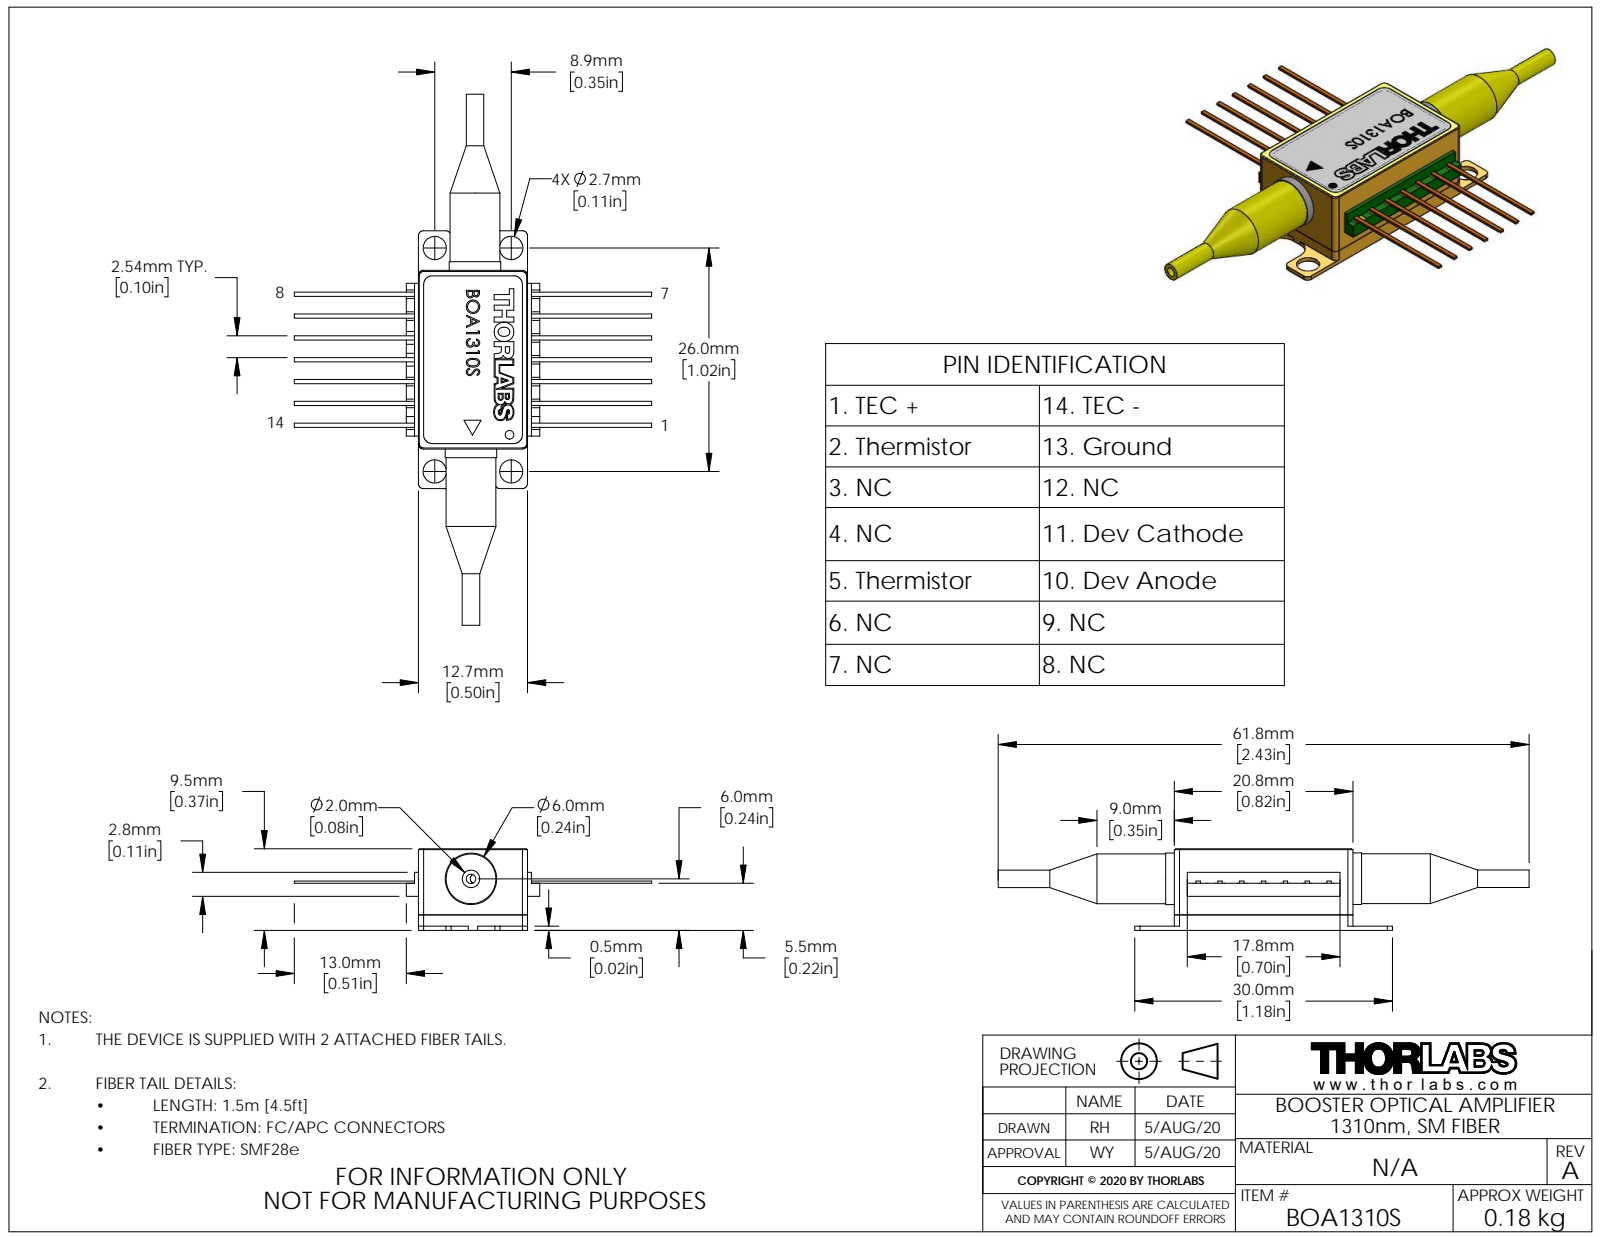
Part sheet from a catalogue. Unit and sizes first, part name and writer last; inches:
Units: inches
Overall size (bounding box): 2.433 × 1.638 × 0.374
Round holes (diameter × count): ⌀0.106 ×4, ⌀0.043 ×2, ⌀0.039 ×1
Round bosses / shafts (diameter × count): ⌀0.236 ×2, ⌀0.228 ×2, ⌀0.08 ×2
Partial cylindrical surfaces — rounded edges, fillets, slot ends (radius × count): R0.024 ×12, R0.02 ×4, R0.079 ×4, R0.039 ×1
Main face-to-face distances: 0.373, 0.5, 0.071, 0.302, 0.146, 0.085, 0.156, 0.217, 0.156, 0.217
Hole centre spacings: 0.35, 1.024, 1.082, 0.019, 0.168, 0.381, 0.856, 0.922
Bodies: 0 solids, 344 faces (241 planar, 51 cylindrical, 52 other)
Part name (STEP PRODUCT): QTN042298-E0W
STEP written by: SolidWorks 2018 (AUTOMOTIVE_DESIGN)
